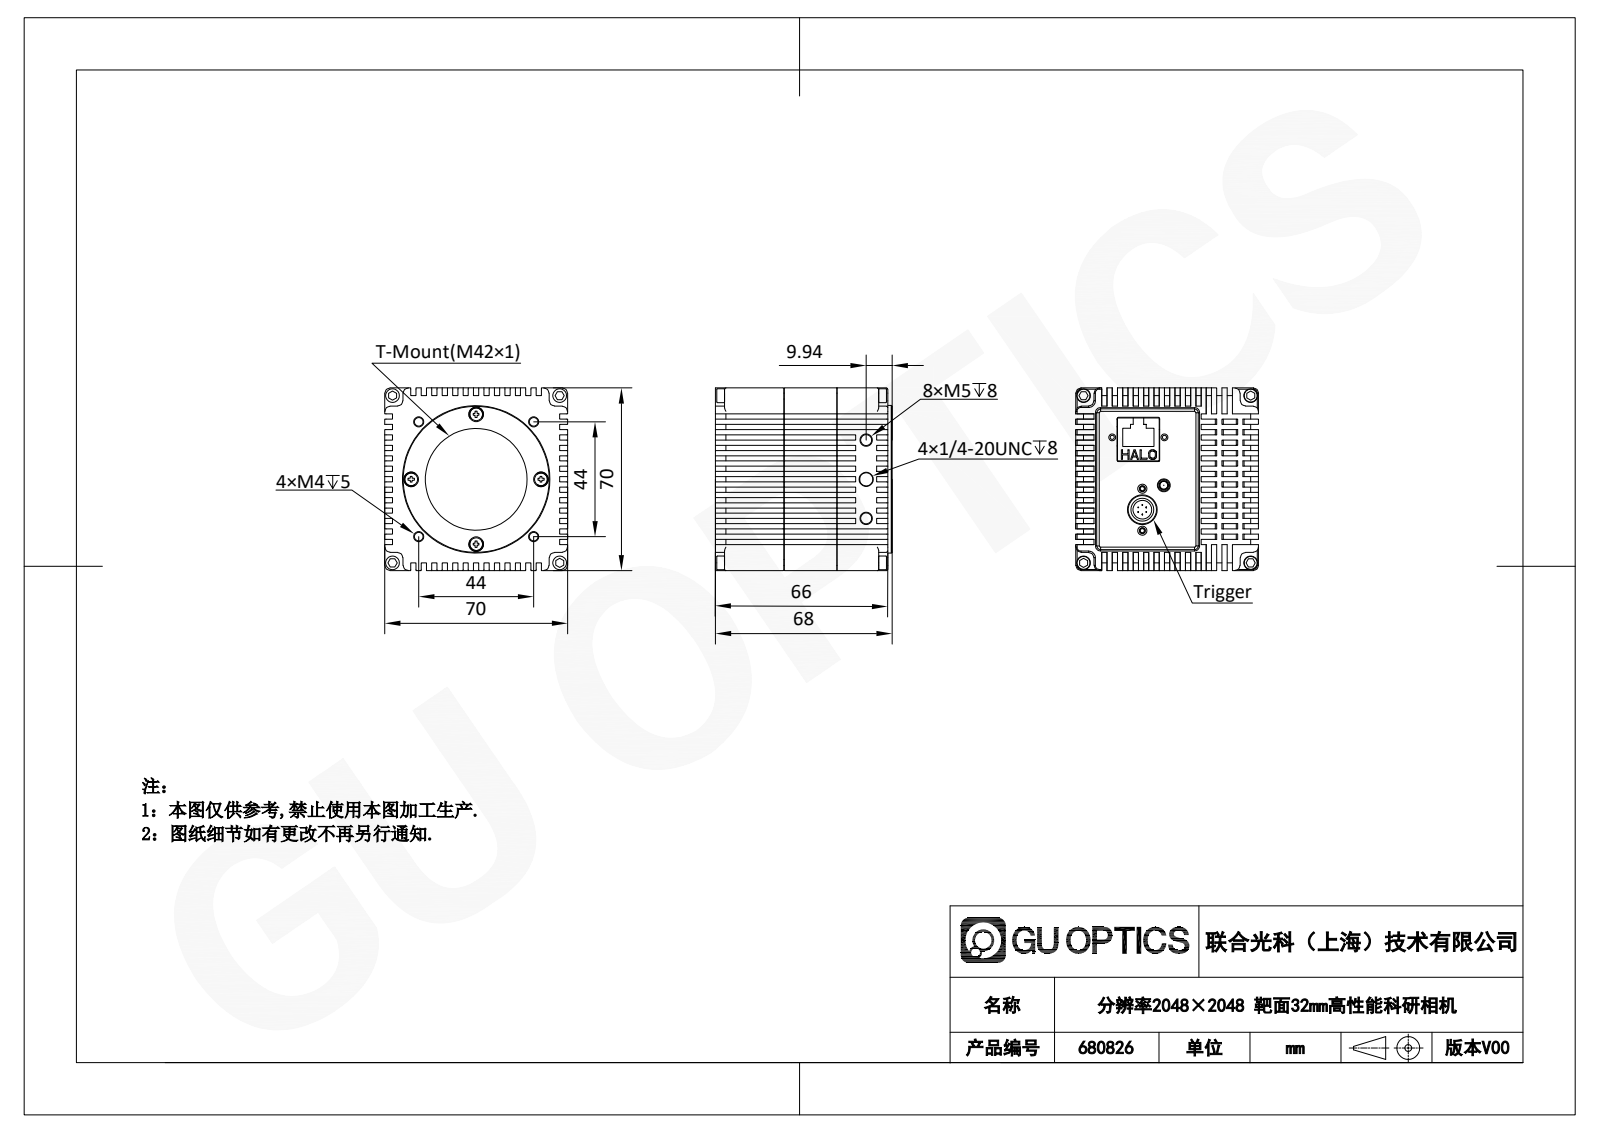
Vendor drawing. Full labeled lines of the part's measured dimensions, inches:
Part name (STEP PRODUCT): SENSOR-_1_ASM_1_ASM; SENSOR-_1_2_1; SENSOR_G400_ASM_5_ASM_1_ASM; M3X5_3_1 (+8 more)
STEP written by: SolidWorks 2024 (CONFIG_CONTROL_DESIGN)
Units: inches
Bodies: 27 solids, 2993 faces (2015 planar, 803 cylindrical, 175 other)
Overall size (bounding box): 2.801 × 2.756 × 2.756
Volume: 5.006 in³ · Surface area: 163.5 in²
Round holes (diameter × count): ⌀0.102 ×8, ⌀0.126 ×8, ⌀0.067 ×4, ⌀0.071 ×4, ⌀0.134 ×4, ⌀0.171 ×4, ⌀0.22 ×4, ⌀0.201 ×2, ⌀0.079 ×1, ⌀0.285 ×1, ⌀0.319 ×1, ⌀1.378 ×1
Round bosses / shafts (diameter × count): ⌀0.018 ×119, ⌀0.118 ×9, ⌀0.02 ×6, ⌀0.217 ×4, ⌀0.209 ×4, ⌀0.197 ×4, ⌀0.126 ×4, ⌀0.091 ×2
Partial cylindrical surfaces — rounded edges, fillets, slot ends (radius × count): R0.02 ×66, R0.039 ×30, R0.079 ×28, R0.016 ×16, R0.118 ×10, R0.004 ×8, R0.008 ×8, R0.059 ×4
Main face-to-face distances: 0.079, 0.197, 0.157, 0.236, 0.118, 2.441, 2.362, 2.638, 0.354, 2.559
Hole centre spacings: 0.873, 0.857, 1.291, 1.713, 2.011, 2.038, 2.146, 2.162
